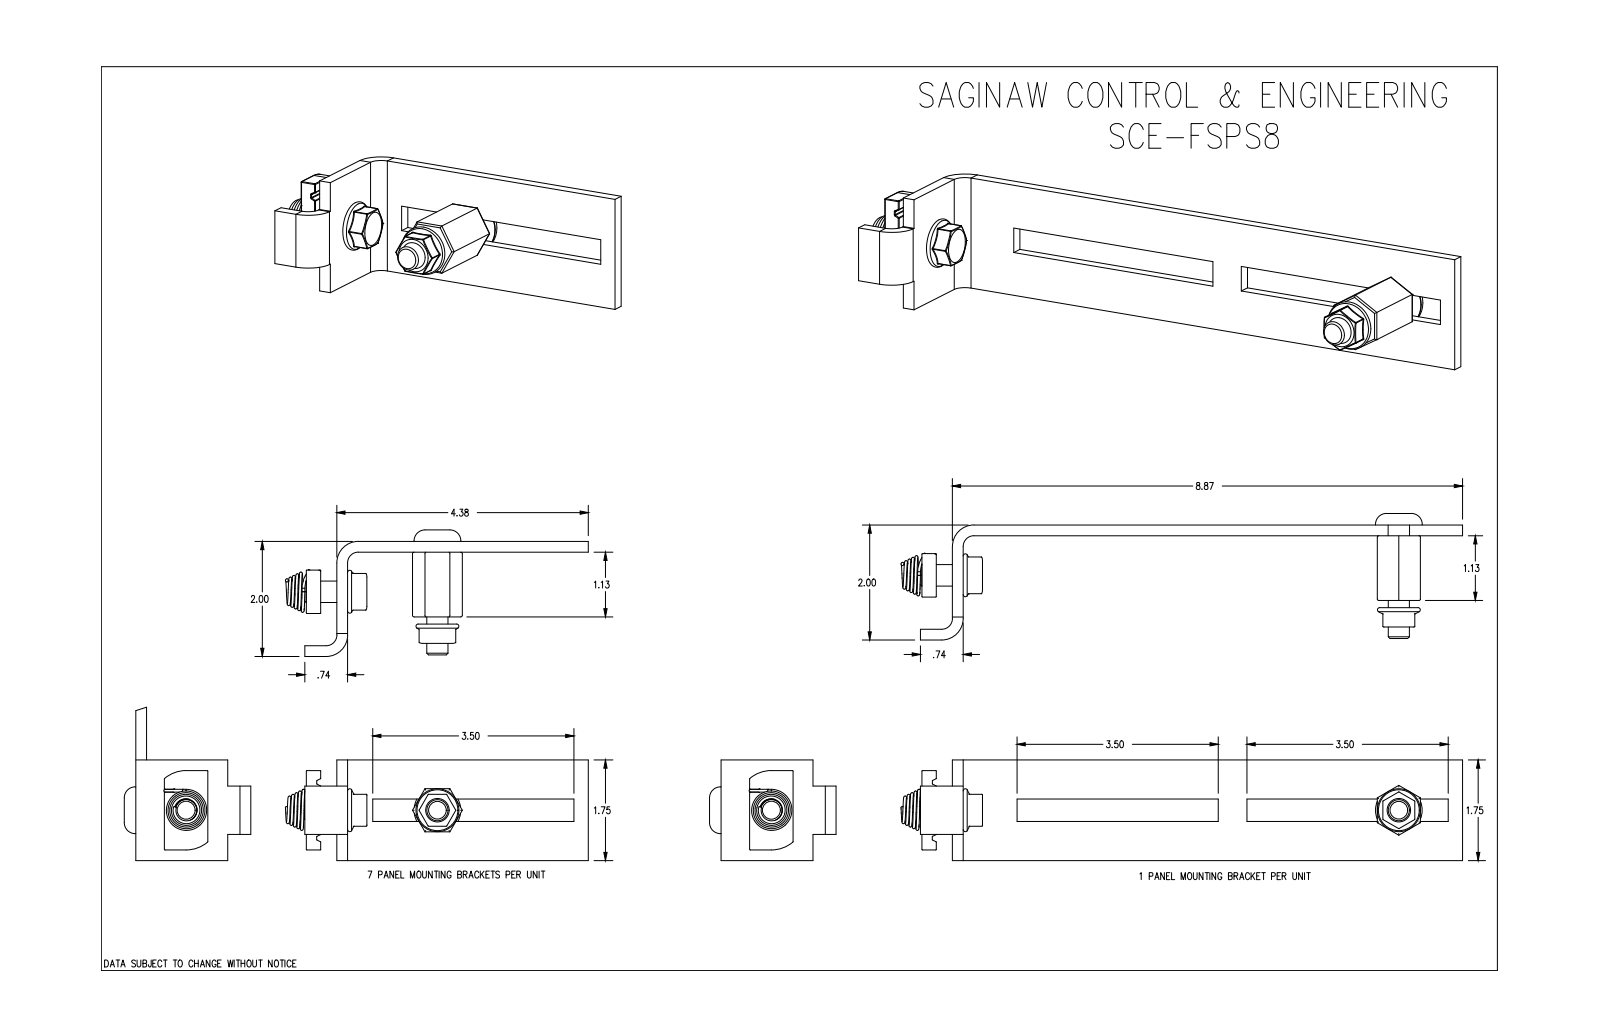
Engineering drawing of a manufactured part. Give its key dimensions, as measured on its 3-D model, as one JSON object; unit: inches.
{"part_name": "SCE-FSPS8", "step_written_by": "SolidWorks 2019 (CONFIG_CONTROL_DESIGN)", "units": "inches", "bodies": {"solids": 48, "faces": 2180, "planar": 604, "cylindrical": 720, "other": 856}, "overall_size": [71.58, 47.538, 2.2], "volume_in3": 24.46, "surface_area_in2": 335, "round_holes": [[0.367, 8], [0.375, 8], [0.375, 6]], "round_bosses_or_shafts": [[0.049, 16], [0.813, 8], [0.368, 8], [0.373, 4]], "partial_cylinders_radius": [[0.01, 350], [0.025, 76], [0.047, 32], [0.187, 8], [0.374, 8], [0.579, 8], [0.188, 6], [0.187, 2]], "face_to_face_distances": [0.187, 45.563, 0.68, 1.07, 0.75, 1.75, 29.13, 45.376, 18.294, 45.75], "hole_center_spacings": [58.255, 29.125, 29.13, 42.25, 21.125, 21.125, 35.984, 51.316]}
